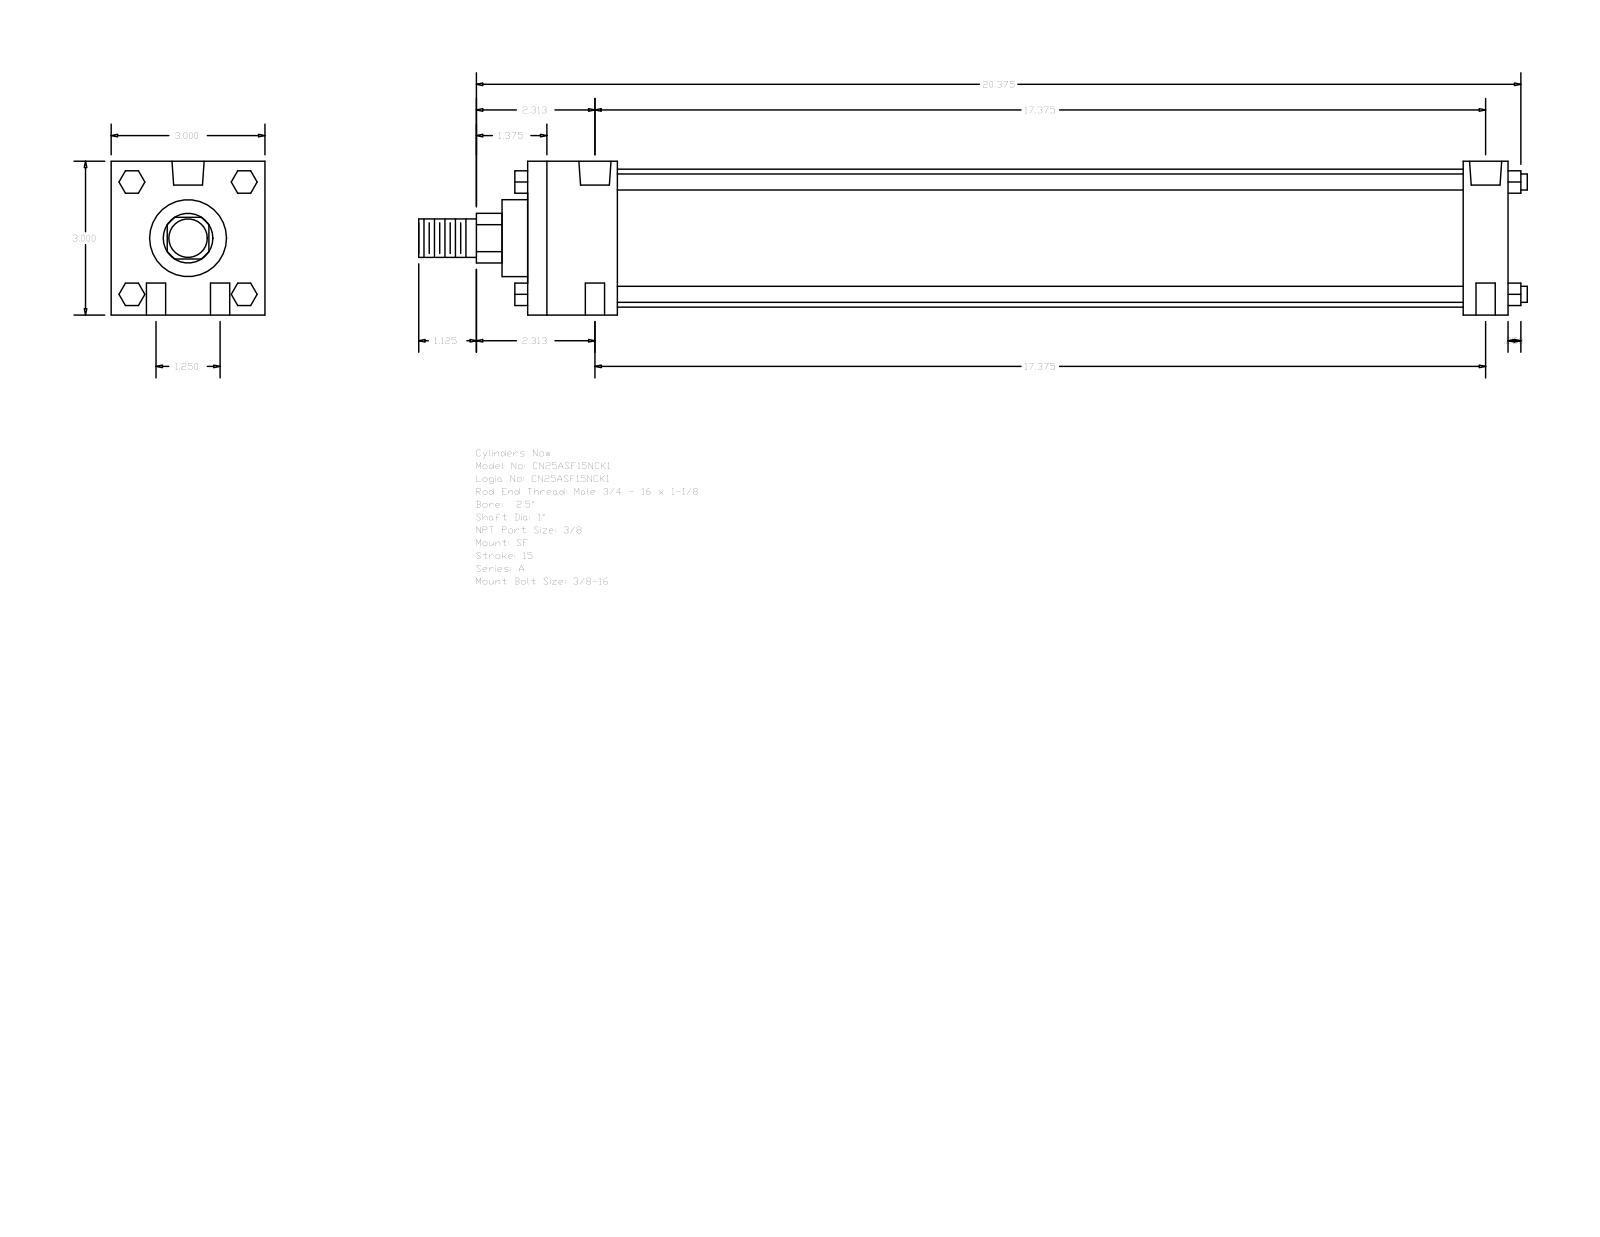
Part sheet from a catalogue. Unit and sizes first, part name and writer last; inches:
Units: inches
Overall size (bounding box): 21.625 × 3 × 3
Round holes (diameter × count): ⌀0.375 ×4, ⌀0.219 ×2, ⌀0.627 ×2
Round bosses / shafts (diameter × count): ⌀0.313 ×4, ⌀2.69 ×1, ⌀1.5 ×1, ⌀1 ×1, ⌀0.75 ×1
Partial cylindrical surfaces — rounded edges, fillets, slot ends (radius × count): R0.484 ×1
Main face-to-face distances: 3, 19.125, 18.25, 0.875, 1.75, 16.5, 17.375, 0.5, 0.437, 2.25
Hole centre spacings: 0.625, 17.386, 17.375, 1.25, 17.42, 17.562
Bodies: 0 solids, 124 faces (94 planar, 30 cylindrical, 0 other)
Part name (STEP PRODUCT): A_SF__0250_1
STEP written by: GSSL Pune (CONFIG_CONTROL_DESIGN)
